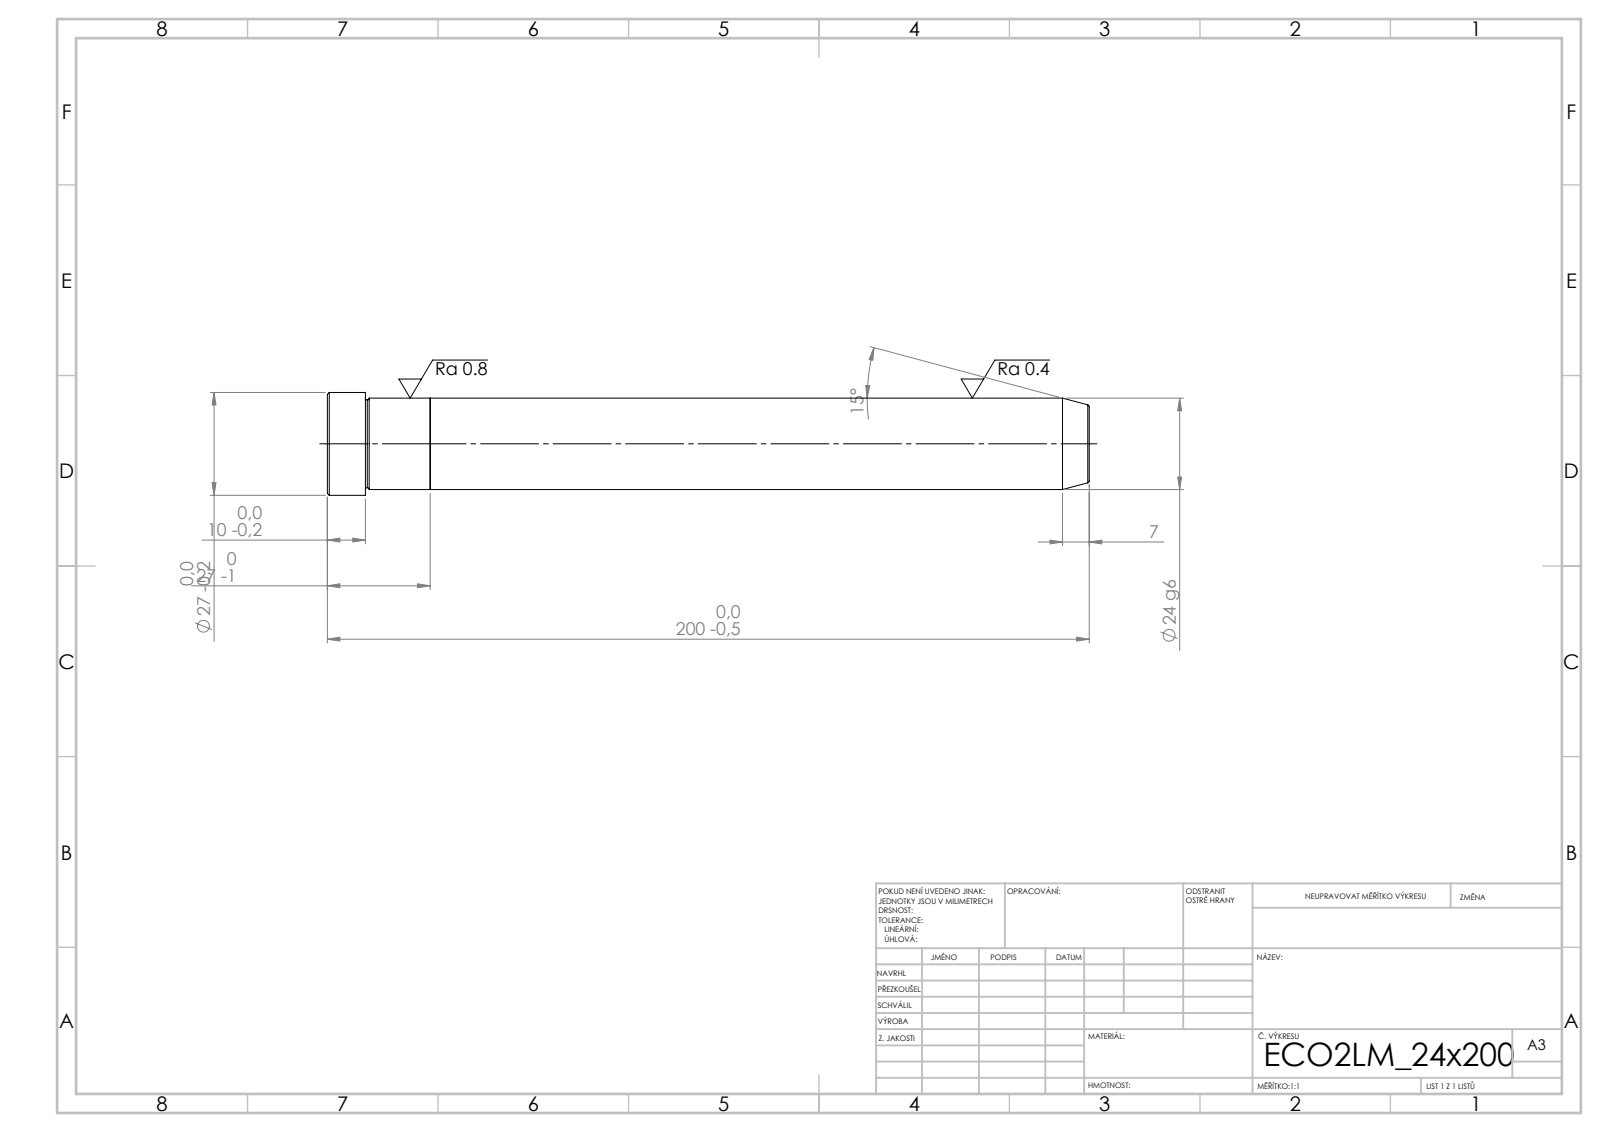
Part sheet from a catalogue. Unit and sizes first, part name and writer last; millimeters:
Units: millimetres
Overall size (bounding box): 200 × 27 × 27
Round bosses / shafts (diameter × count): ⌀27 ×1, ⌀24 ×1
Main face-to-face distances: 27, 173, 200, 190, 17, 10
Volume: 91 169 mm³ · Surface area: 17 077 mm²
Bodies: 2 solids, 21 faces (5 planar, 6 cylindrical, 10 other)
STEP written by: SolidWorks 2019 (CONFIG_CONTROL_DESIGN)
